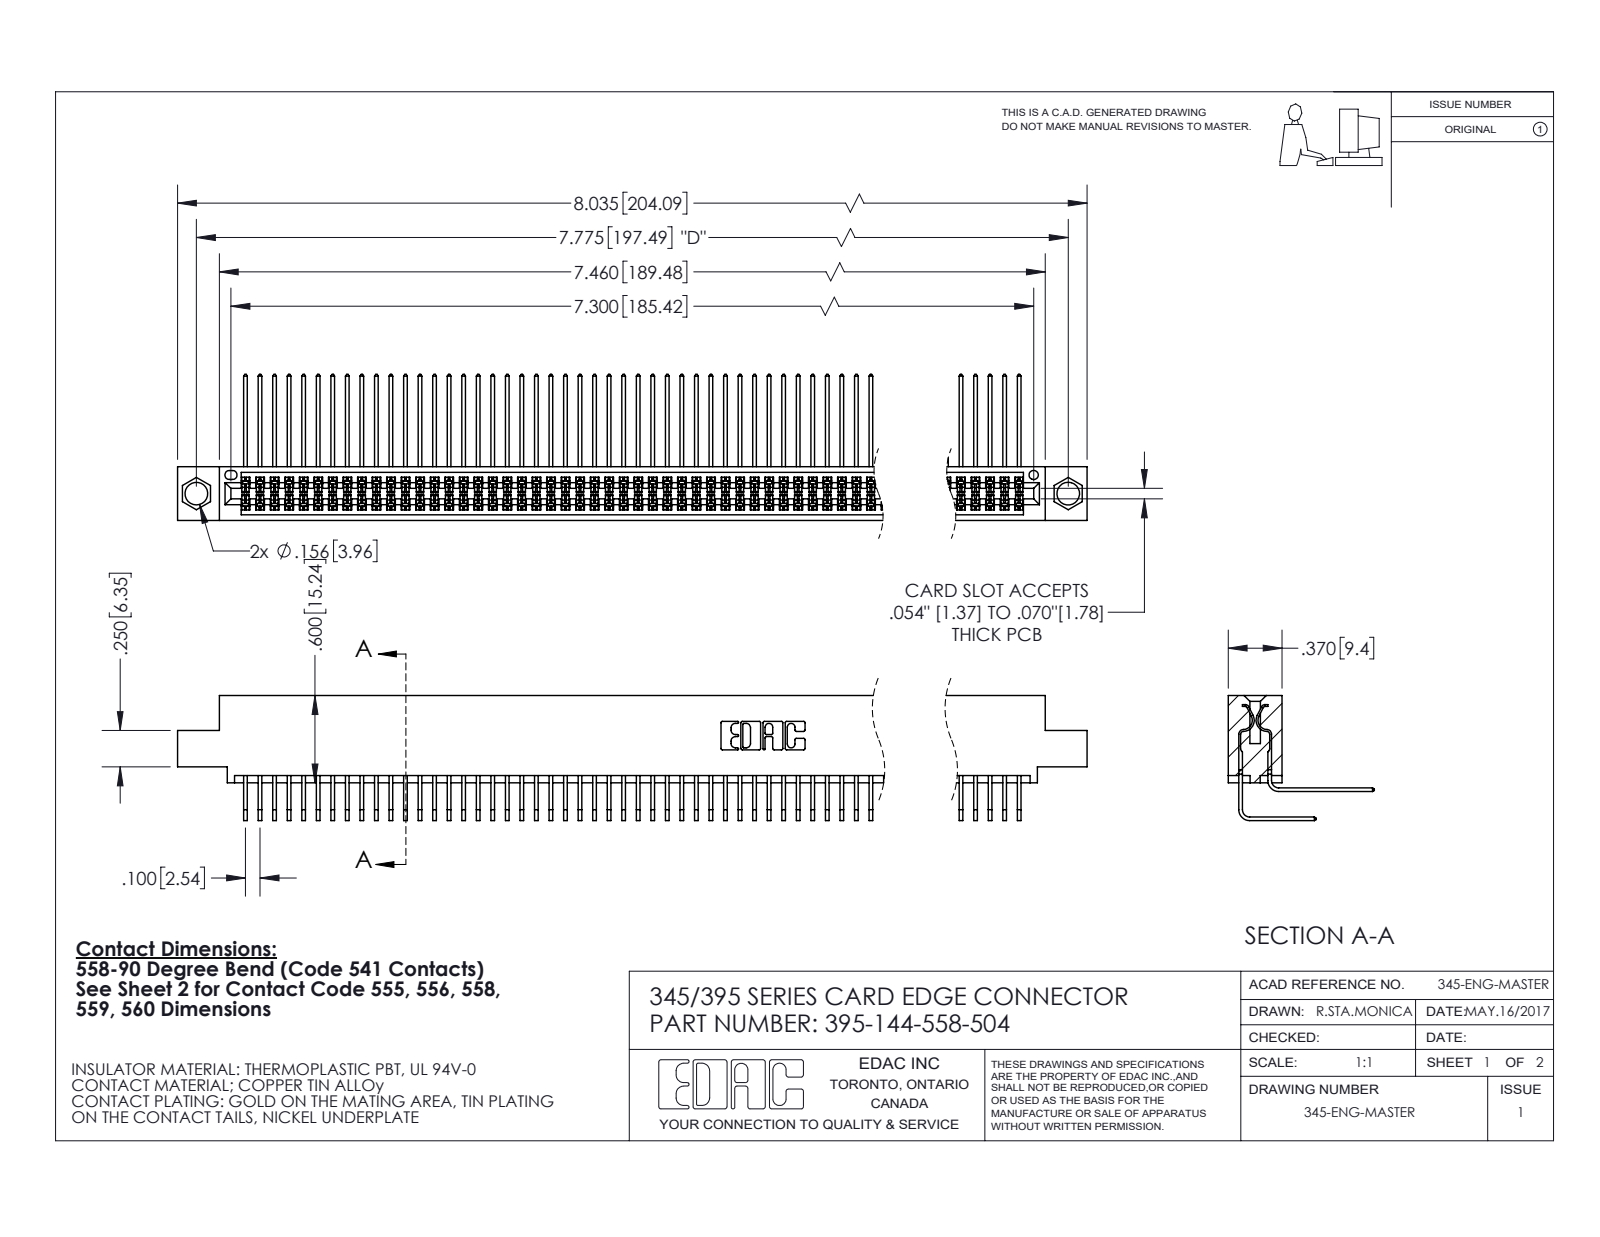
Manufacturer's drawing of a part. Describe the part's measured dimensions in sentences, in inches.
The part is named "345-292-001_558 Tail - 2; 345-292-001_558 559 Tail - 1; 395-144-558-504; 345 Part_0.110 Offset - 0.156 Dia-TI". Its 3-D file was written by "SolidWorks 2020 (CONFIG_CONTROL_DESIGN)". It is 145 solids with 7632 faces: 5138 planar, 2494 cylindrical and 0 other. Overall it measures 8.035 by 1.005 by 0.859 inches. Its volume is 1.267 cubic inches and its surface area 54.42 square inches. Round holes: 2 of diameter 0.156, 1 of diameter 0.064. Partial cylindrical surfaces (rounded edges, fillets, slot ends): 217 of radius 0.006, 22 of radius 0.01, 6 of radius 0.007, 6 of radius 0.031, 3 of radius 0.026, 2 of radius 0.014, 2 of radius 0.019, 2 of radius 0.022. The main face-to-face distances are 0.072, 0.298, 0.2, 0.37, 0.098, 0.272, 0.025, 0.225, 0.025, 0.175. The hole center spacings are 0.27, 7.539, 7.775.
